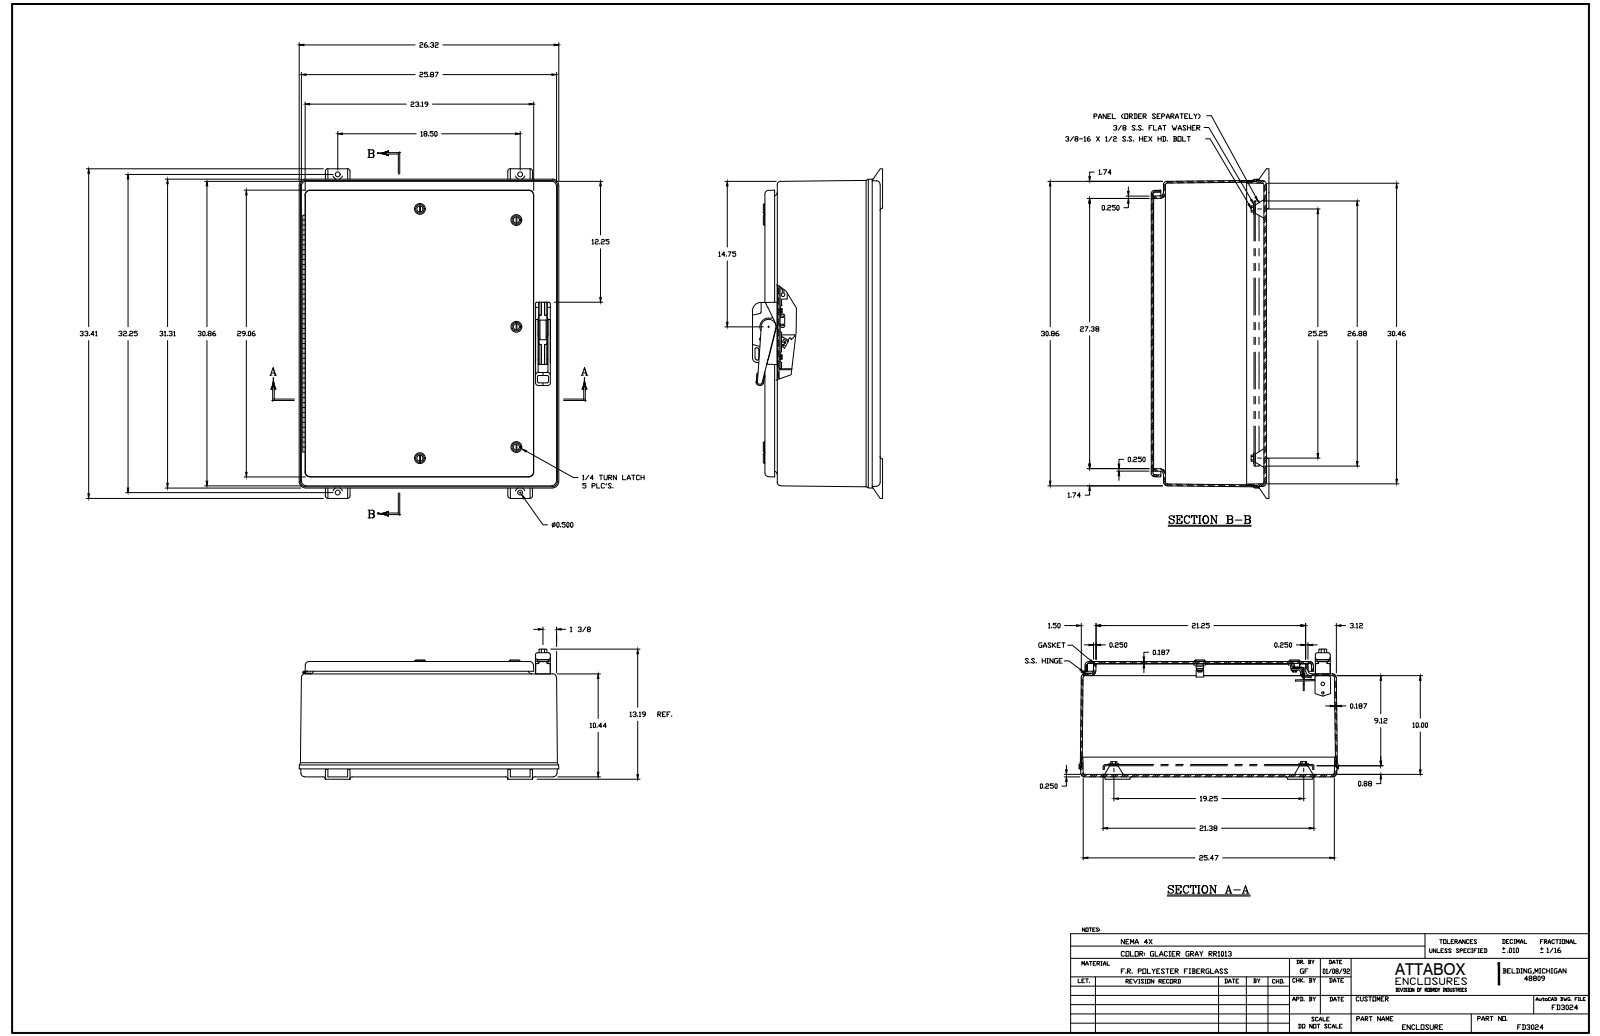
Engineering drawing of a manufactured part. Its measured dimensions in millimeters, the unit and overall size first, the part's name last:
Units: millimetres
Overall size (bounding box): 848.6 × 668.3 × 335
Round holes (diameter × count): ⌀3.8 ×13, ⌀4.7 ×8, ⌀12.7 ×8, ⌀16 ×5, ⌀22.5 ×5, ⌀4.3 ×4, ⌀5.5 ×4, ⌀6.5 ×4, ⌀7.1 ×4, ⌀7.8 ×4, ⌀7.9 ×4, ⌀11 ×4
Round bosses / shafts (diameter × count): ⌀7.6 ×8, ⌀5.1 ×7, ⌀27.8 ×5, ⌀16 ×5, ⌀7 ×5, ⌀25.4 ×4, ⌀9.5 ×4, ⌀9.1 ×4
Partial cylindrical surfaces — rounded edges, fillets, slot ends (radius × count): R6.4 ×37, R3.2 ×20, R4 ×19, R4.8 ×16, R8 ×14, R12.7 ×12, R9.5 ×10, R4.7 ×9
Main face-to-face distances: 4.7, 6.4, 292, 285.7, 4.7, 296.8, 290.4, 25.5, 3.3, 31.9
Hole centre spacings: 182.5, 0.4, 7.1, 163.9, 218.4, 274.7, 309.5, 365
Volume: 12 220 000 mm³ · Surface area: 5 143 000 mm²
Bodies: 93 solids, 2777 faces (1378 planar, 784 cylindrical, 615 other)
Part name (STEP PRODUCT): FD3024
STEP written by: SolidWorks 2018 (AUTOMOTIVE_DESIGN)
